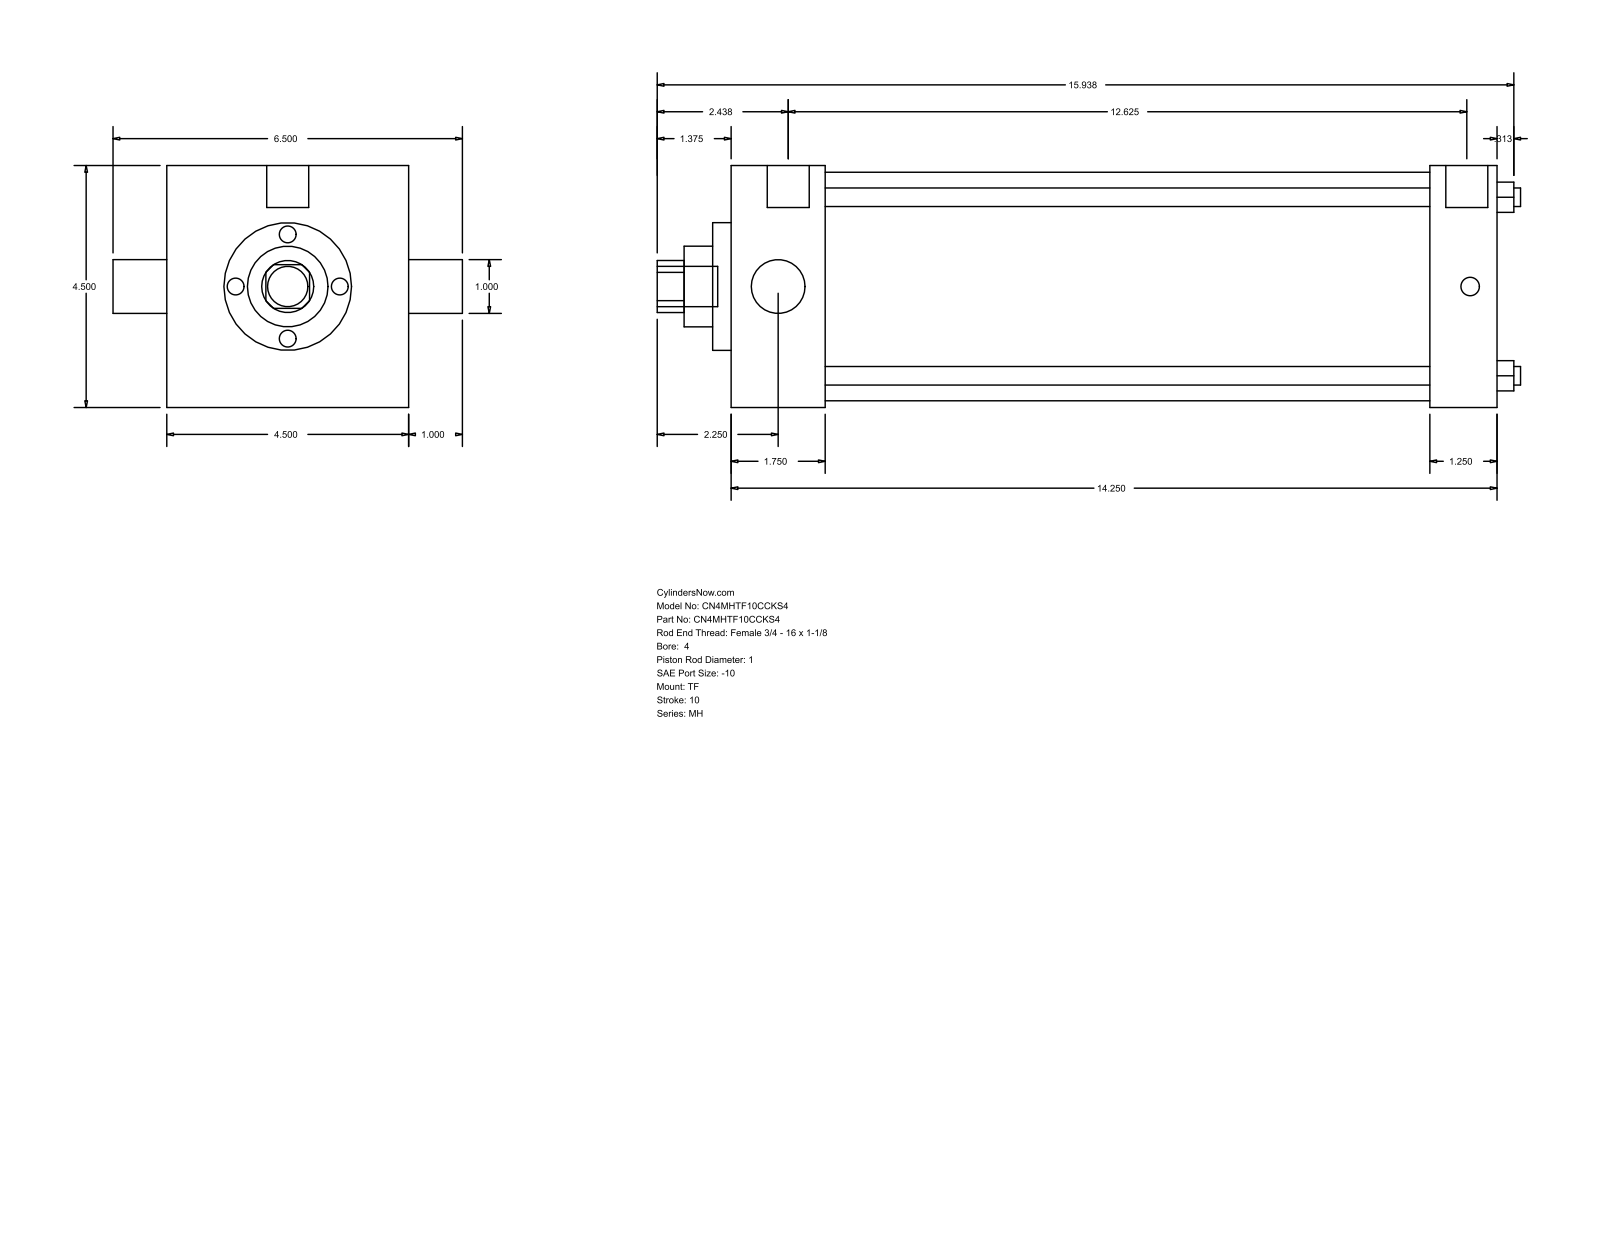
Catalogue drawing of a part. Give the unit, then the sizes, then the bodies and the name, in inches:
Units: inches
Overall size (bounding box): 16.063 × 6.5 × 4.5
Round holes (diameter × count): ⌀0.345 ×4, ⌀1 ×2, ⌀1.5 ×1, ⌀2.375 ×1, ⌀4.25 ×1
Round bosses / shafts (diameter × count): ⌀0.344 ×3, ⌀0.781 ×2, ⌀0.75 ×1
Partial cylindrical surfaces — rounded edges, fillets, slot ends (radius × count): R0.484 ×1
Main face-to-face distances: 4.5, 14.25, 1.75, 12.5, 13, 11.25, 1.25, 0.344, 2.094, 13.344
Hole centre spacings: 2.347, 3.32, 4.695
Bodies: 0 solids, 86 faces (61 planar, 25 cylindrical, 0 other)
Part name (STEP PRODUCT): MH_TF__0400_1
STEP written by: GSSL Pune (CONFIG_CONTROL_DESIGN)
